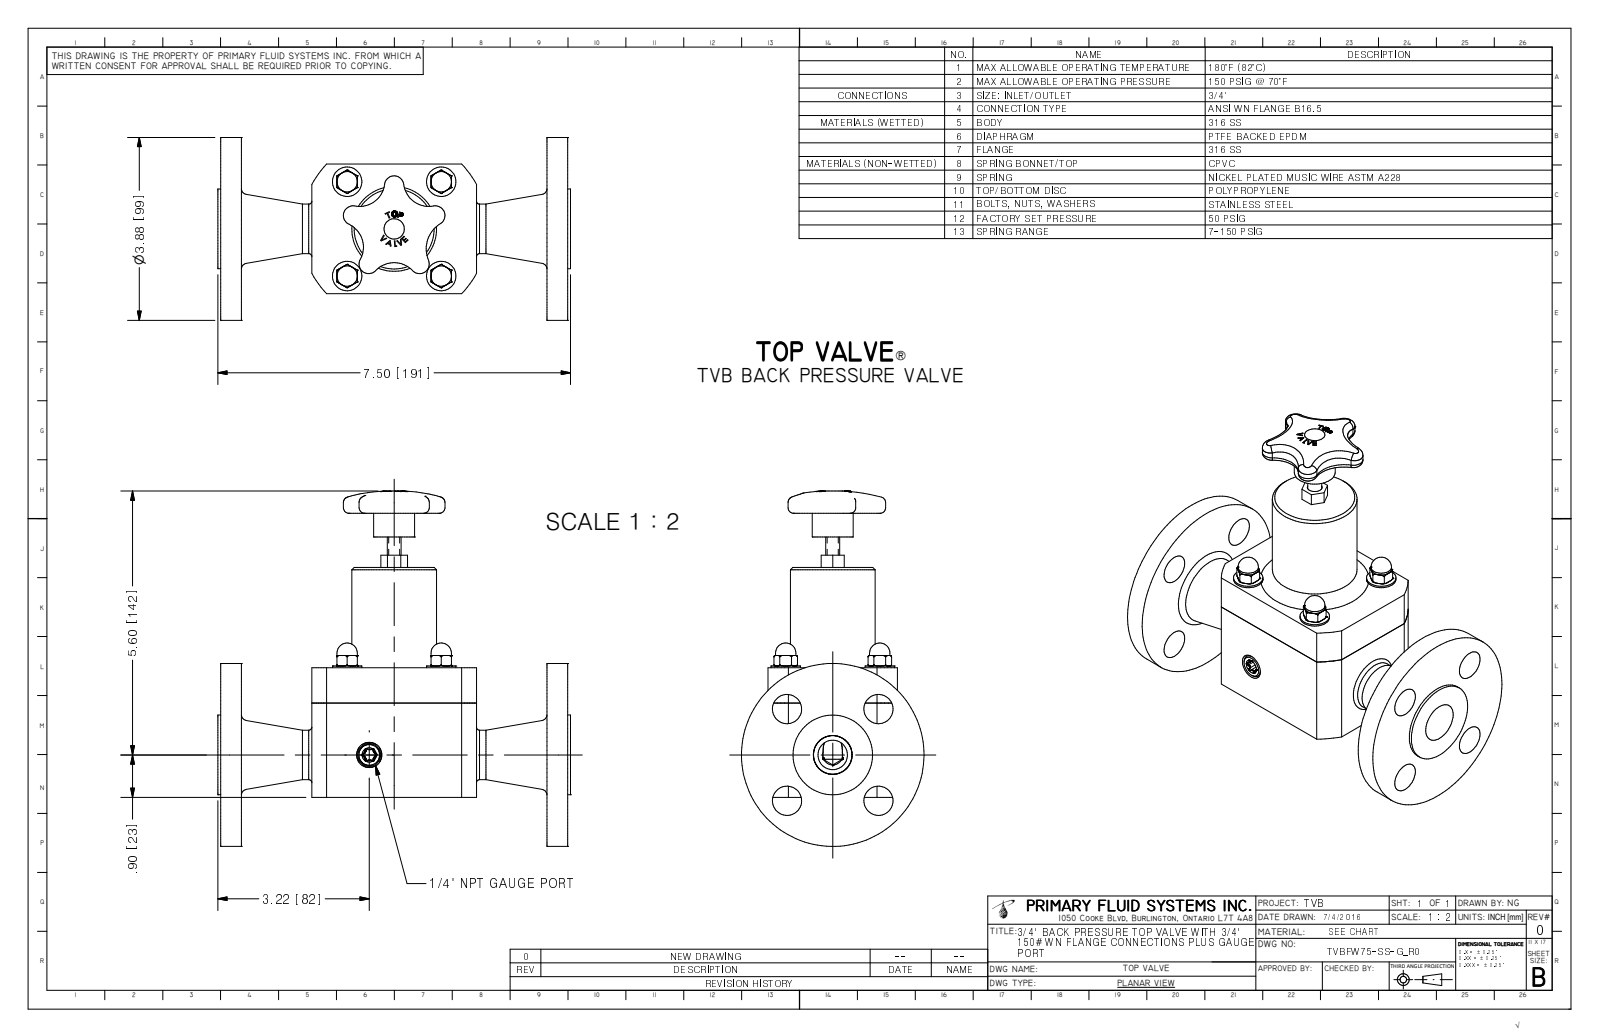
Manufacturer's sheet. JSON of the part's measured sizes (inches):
{"part_name": "TVBFW75-SS-G-R0", "step_written_by": "Autodesk Inventor 2009 (AUTOMOTIVE_DESIGN)", "units": "inches", "bodies": {"solids": 1, "faces": 383, "planar": 158, "cylindrical": 65, "other": 160}, "overall_size": [7.537, 7.5, 3.88], "volume_in3": 43.94, "surface_area_in2": 155.7, "round_holes": [[0.175, 4], [0.62, 4], [0.824, 1]], "round_bosses_or_shafts": [[0.625, 4], [0.433, 4], [0.375, 4], [3.88, 1], [1.8, 1], [1.69, 1], [1.05, 1], [0.87, 1]], "partial_cylinders_radius": [[0.027, 6], [0.085, 5], [0.205, 5], [0.536, 4], [0.656, 4], [0.625, 1], [0.745, 1], [1.988, 1]], "face_to_face_distances": [0.44, 6.935, 5.437, 1.937, 1.498, 4.998, 7.375, 6.495, 2.75, 3.5], "hole_center_spacings": [1.375, 1.945, 2, 2.75, 2.828]}
